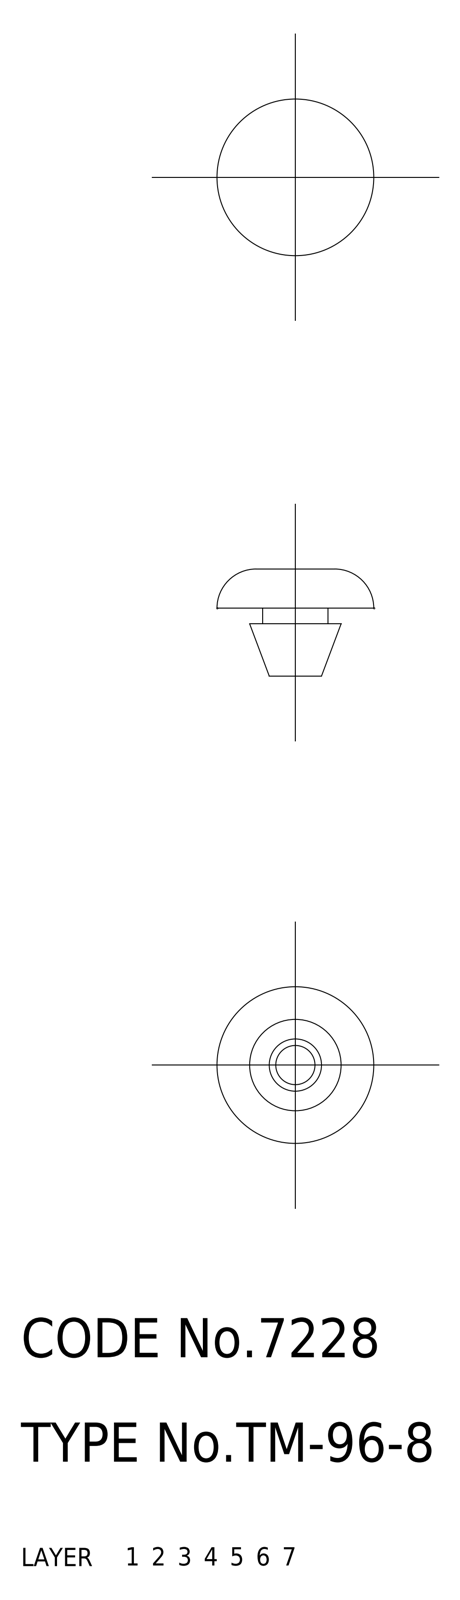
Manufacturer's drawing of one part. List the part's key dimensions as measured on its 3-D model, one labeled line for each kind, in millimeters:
Part name (STEP PRODUCT): cushion
STEP written by: CADfix (AUTOMOTIVE_DESIGN)
Units: millimetres
Bodies: 1 solid, 13 faces (0 planar, 0 cylindrical, 13 other)
Overall size (bounding box): 12 × 12 × 8.2
Volume: 359 mm³ · Surface area: 440 mm²
